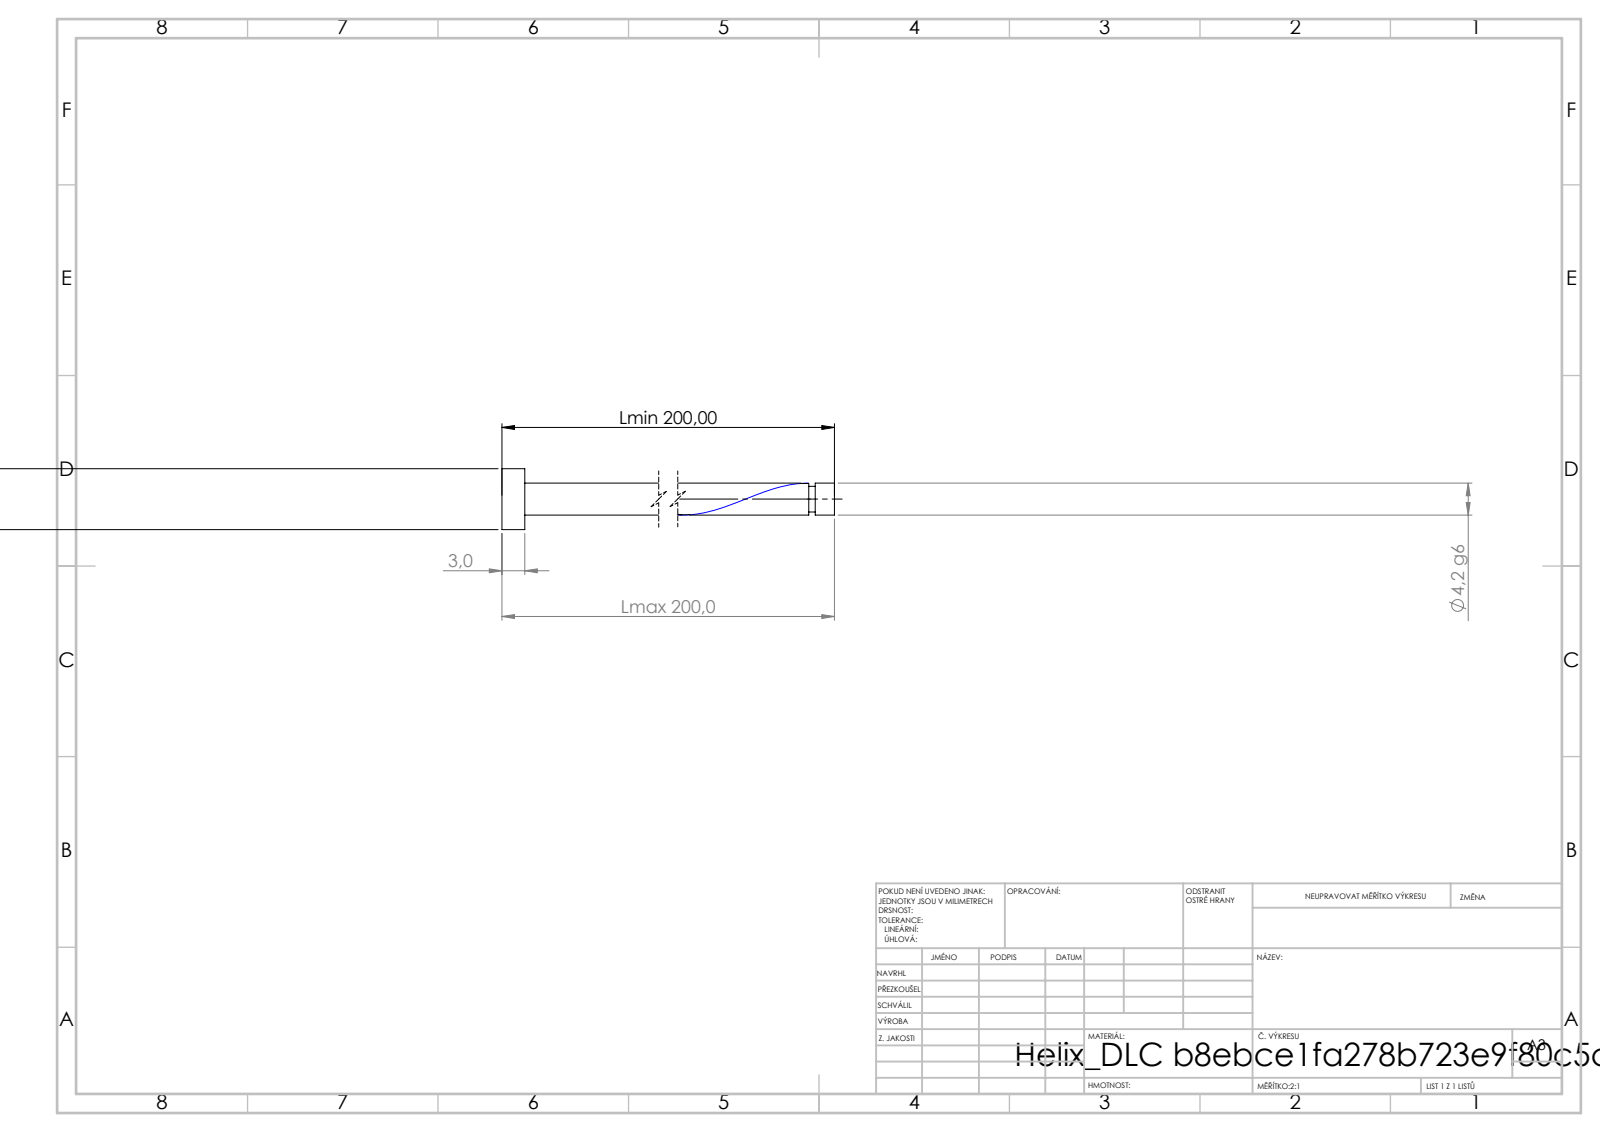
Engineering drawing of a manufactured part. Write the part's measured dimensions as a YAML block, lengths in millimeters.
step_written_by: "SolidWorks 2019 (CONFIG_CONTROL_DESIGN)"
units: millimeters
bodies: {solids: 1, faces: 21, planar: 6, cylindrical: 14, other: 1}
overall_size: [200, 8, 8]
volume: 2849
surface_area: 2827
round_bosses_or_shafts:
  - {diameter: 8, count: 1}
  - {diameter: 4.2, count: 1}
  - {diameter: 3.36, count: 1}
face_to_face_distances: [3, 200, 197, 197.47, 194.47, 2.53, 196.63, 193.63, 0.84, 3.37]
